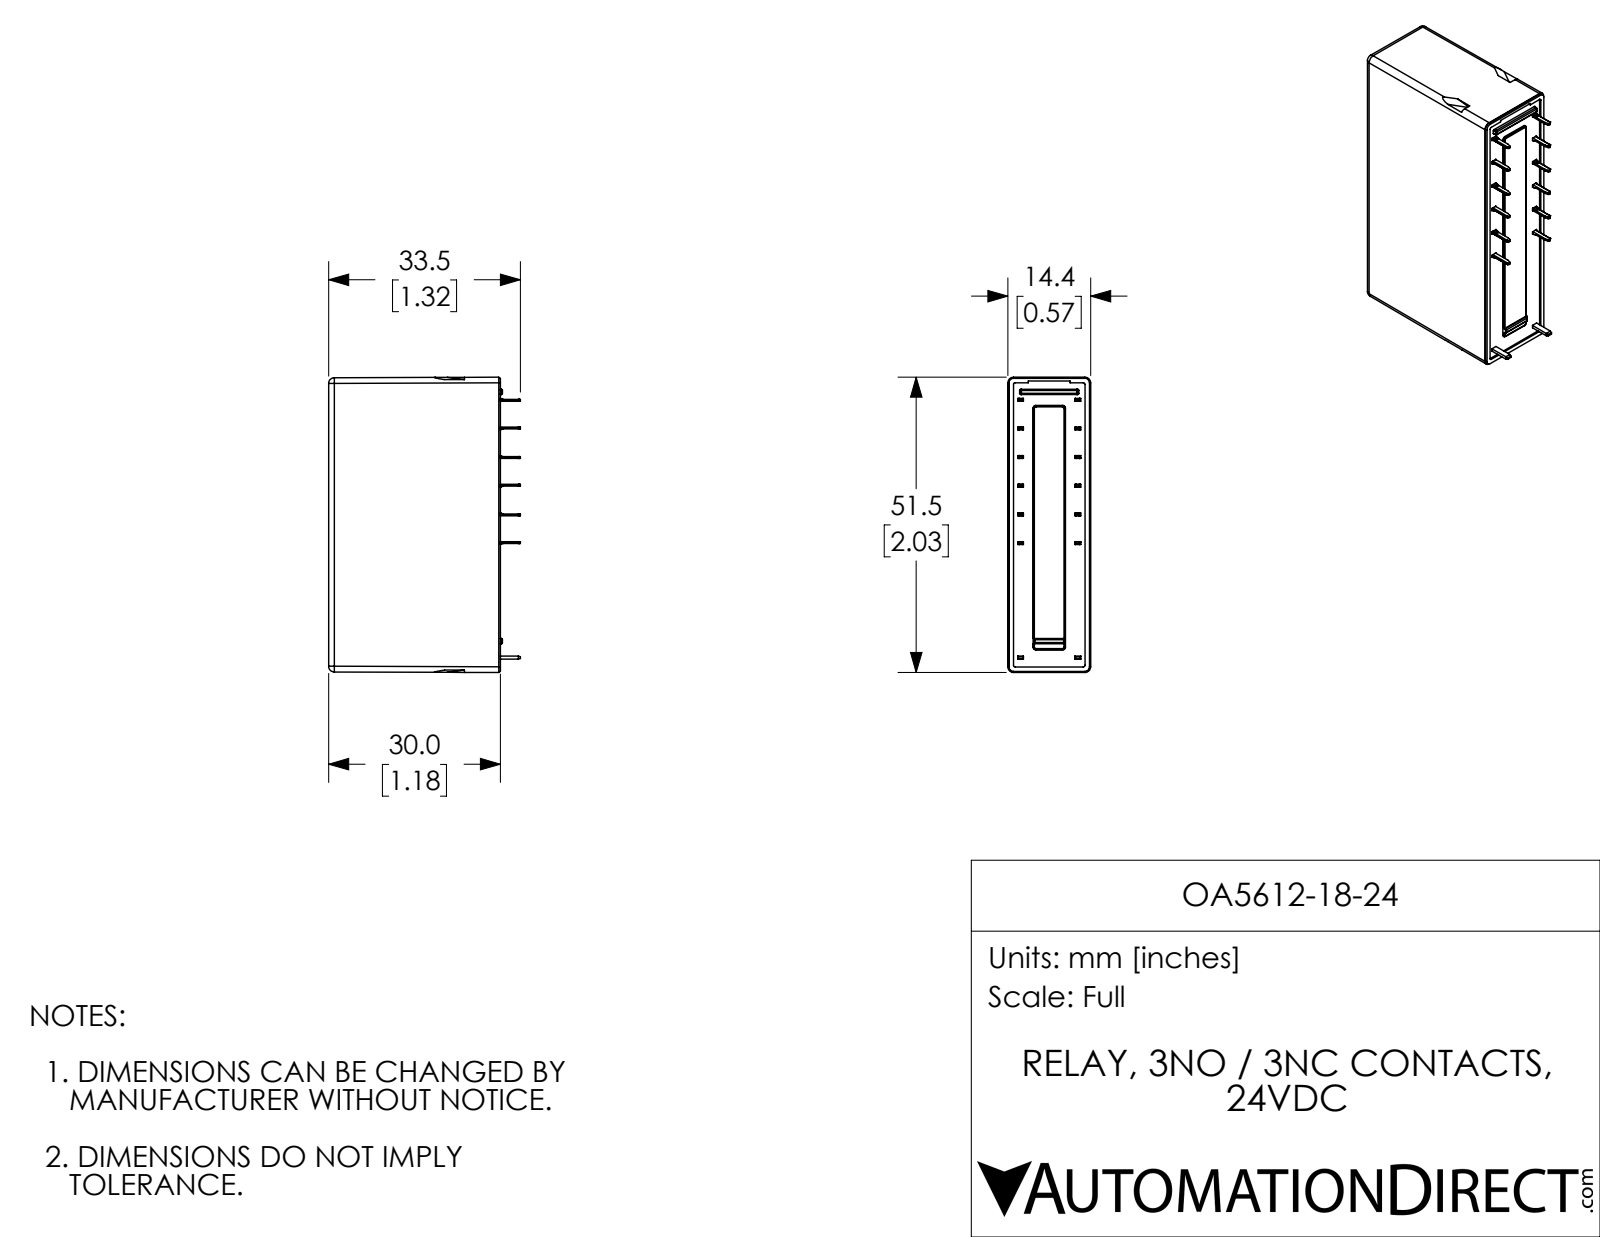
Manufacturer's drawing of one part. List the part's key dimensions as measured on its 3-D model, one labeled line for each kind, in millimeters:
Part name (STEP PRODUCT): OA5612-18-24
STEP written by: SolidWorks 2017 (AUTOMOTIVE_DESIGN)
Units: millimetres
Bodies: 1 solid, 434 faces (262 planar, 126 cylindrical, 46 other)
Overall size (bounding box): 51.5 × 33.5 × 14.5
Volume: 21 990 mm³ · Surface area: 5 512 mm²
Round bosses / shafts (diameter × count): ⌀0.8 ×1
Partial cylindrical surfaces — rounded edges, fillets, slot ends (radius × count): R0.2 ×36, R0.2 ×16, R0.5 ×16, R1 ×8, R0.3 ×4, R0.1 ×2, R0.3 ×2
Main face-to-face distances: 29.7, 30, 10, 0.4, 10.8, 4.8, 0.3, 12.5, 1.7, 0.9
